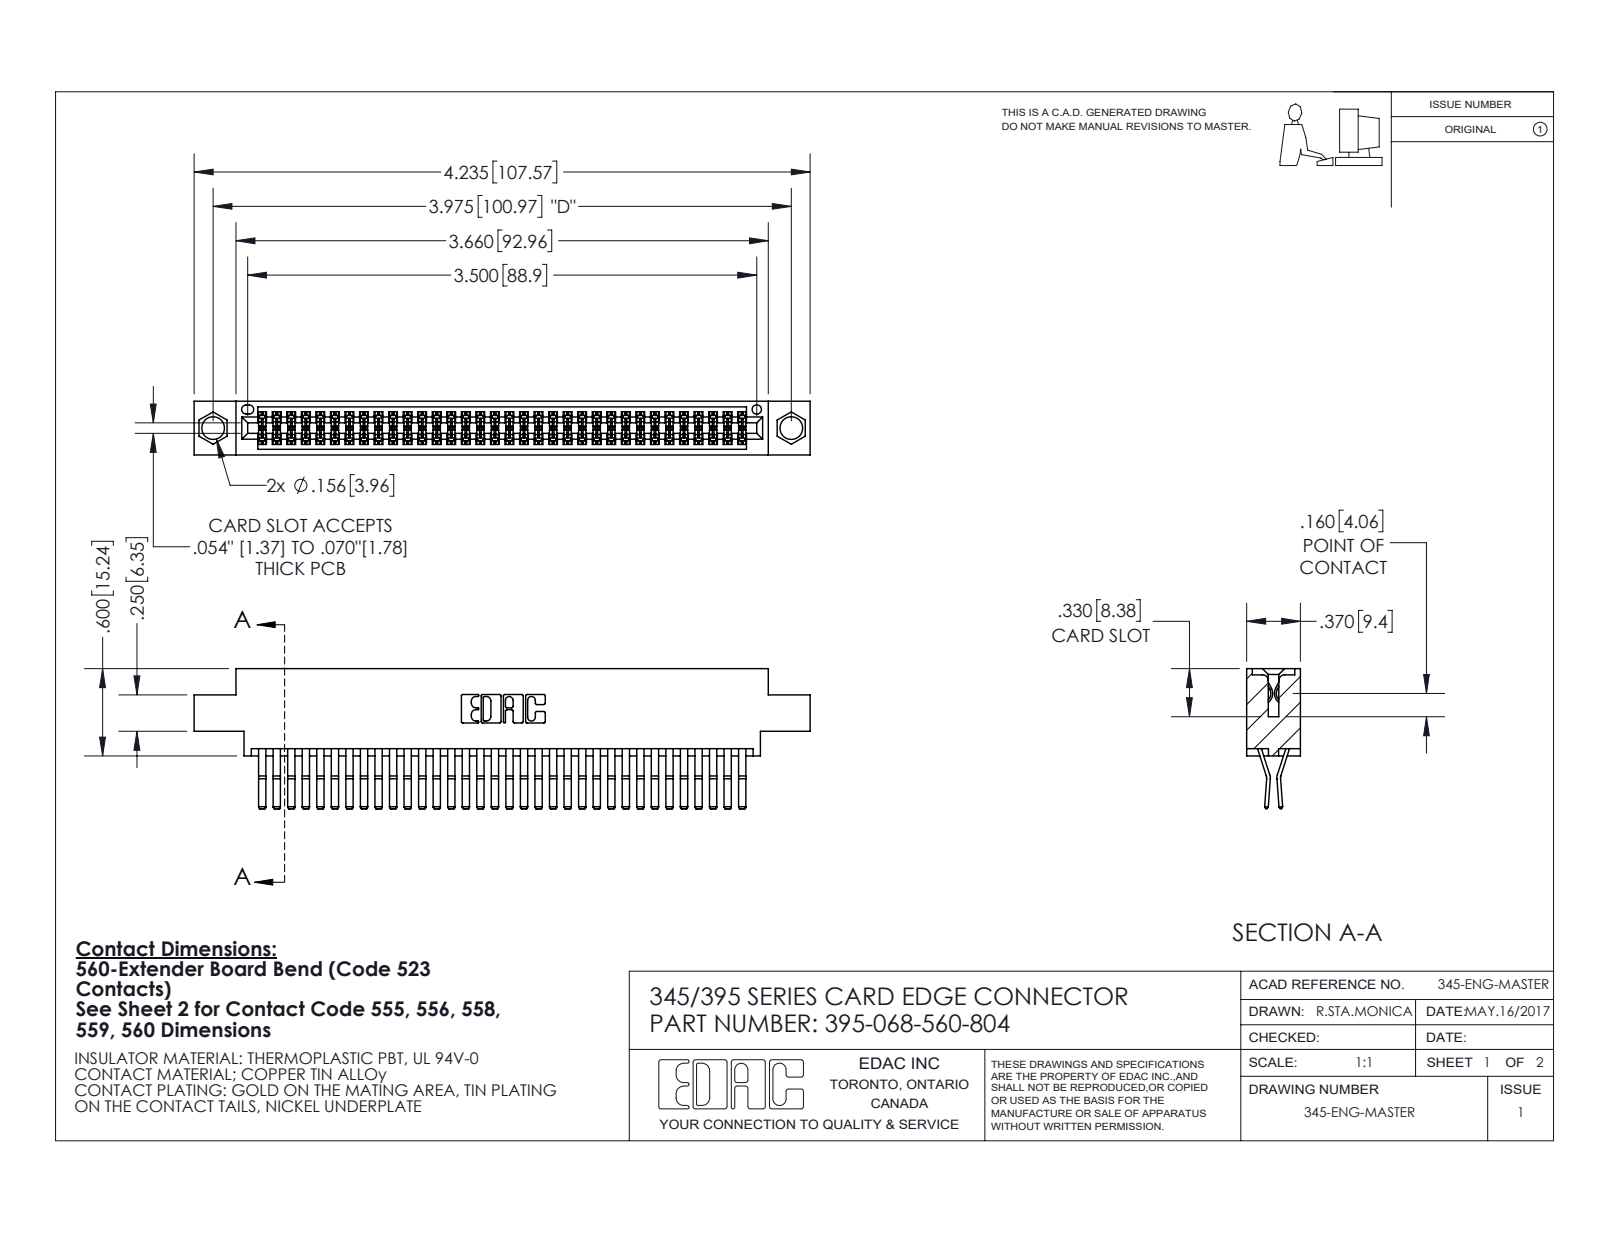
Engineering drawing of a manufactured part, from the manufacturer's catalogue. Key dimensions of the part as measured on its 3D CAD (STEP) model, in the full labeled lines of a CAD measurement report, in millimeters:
Part name (STEP PRODUCT): 395-068-560-804; 345 Part_0.170 Offset - 0.156 Dia-TI; 345-292-001_560 Tail
STEP written by: SolidWorks 2020 (CONFIG_CONTROL_DESIGN)
Units: millimetres
Bodies: 69 solids, 3680 faces (2342 planar, 1338 cylindrical, 0 other)
Overall size (bounding box): 107.6 × 24.4 × 9.4
Volume: 10 600 mm³ · Surface area: 16 660 mm²
Round holes (diameter × count): ⌀4 ×2, ⌀1.6 ×1
Partial cylindrical surfaces — rounded edges, fillets, slot ends (radius × count): R0.2 ×102, R0.3 ×22, R0.2 ×6, R0.8 ×6, R0.7 ×3, R0.3 ×2, R0.4 ×2, R0.5 ×2
Main face-to-face distances: 0.6, 7.6, 1.8, 9.4, 5.1, 2.5, 6.9, 5.7, 4.4, 3.8
Hole centre spacings: 6.9, 95, 101
